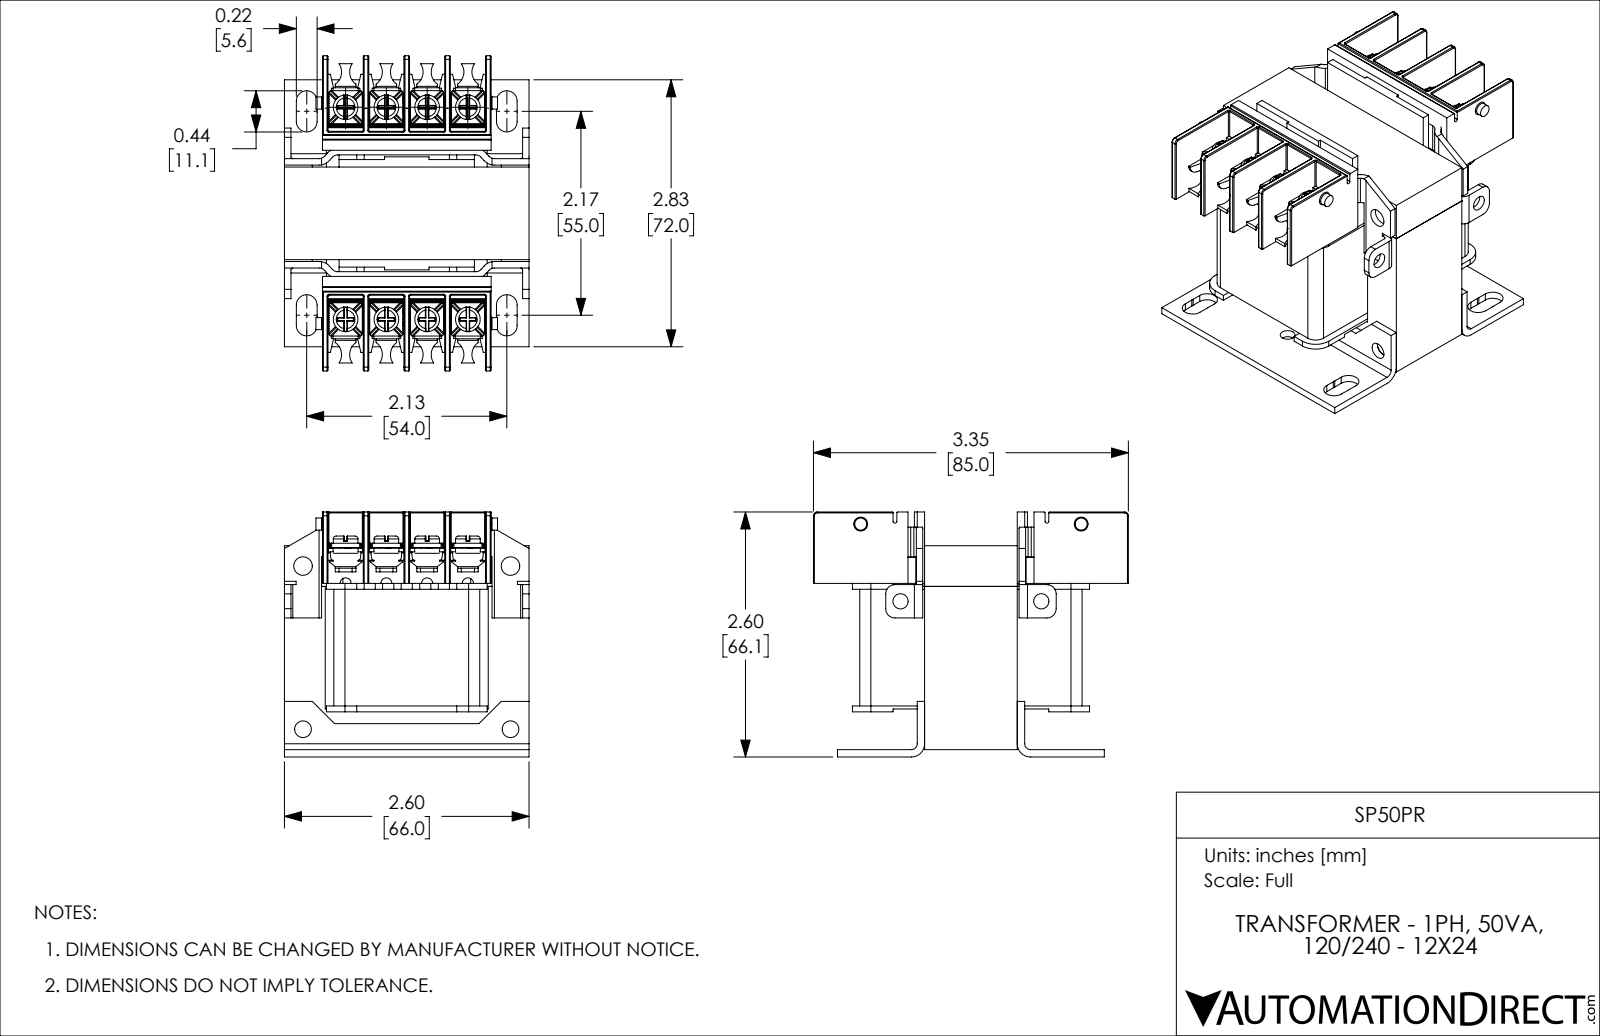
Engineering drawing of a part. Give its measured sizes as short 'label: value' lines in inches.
name: SP50PR
written by: SolidWorks 2018 (AUTOMOTIVE_DESIGN)
unit: in
bodies: 41 solids, 3078 faces (1860 planar, 926 cylindrical, 292 other)
size: 3.346 × 2.601 × 2.598
volume: 9.38 in³; area: 117.4 in²
holes: 10× ⌀0.157, 8× ⌀0.105, 8× ⌀0.138, 2× ⌀0.161, 2× ⌀0.177, 2× ⌀0.197
bosses: 8× ⌀0.262, 8× ⌀0.24, 8× ⌀0.168, 8× ⌀0.11, 3× ⌀0.128
rounds: 52× R0.005, 52× R0.01, 46× R0.012, 32× R0.029, 16× R0.157, 14× R0.039, 12× R0.035, 10× R0.079
face distances: 0.433, 1.732, 0.866, 0.404, 0.463, 0.03, 1.299, 0.059, 1.329, 0.984
hole spacings: 0.433, 0.866, 2.283, 1.299, 2.242, 2.404, 2.274, 2.293
